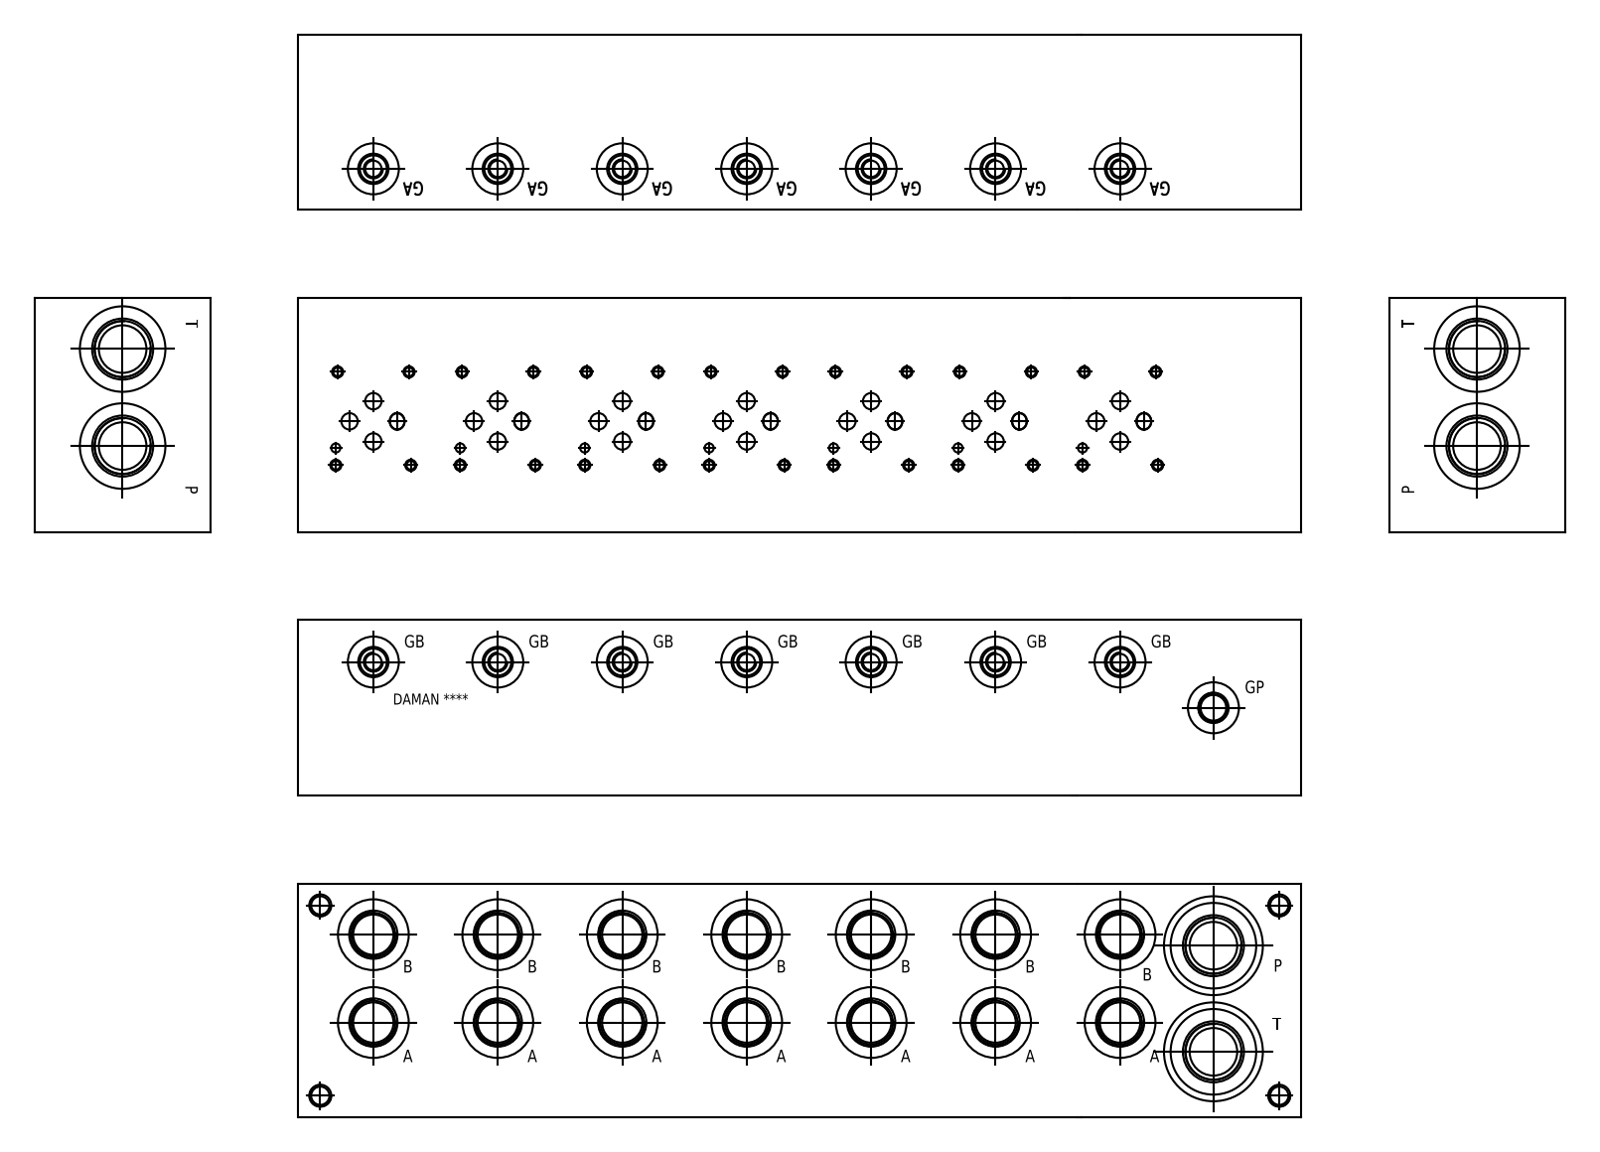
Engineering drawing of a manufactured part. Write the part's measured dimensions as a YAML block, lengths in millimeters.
part_name: "Part_AD03PB072B_3D"
step_written_by: "Autodesk Inventor 2020 (AUTOMOTIVE_DESIGN)"
units: millimeters
bodies: {solids: 1, faces: 1803, planar: 881, cylindrical: 241, other: 681}
overall_size: [434.98, 101.6, 76.2]
volume: 3079000
surface_area: 232554
round_holes:
  - {diameter: 7.14, count: 35}
  - {diameter: 4.22, count: 28}
  - {diameter: 5, count: 28}
  - {diameter: 11.68, count: 15}
  - {diameter: 13.26, count: 15}
  - {diameter: 22.12, count: 15}
  - {diameter: 17.48, count: 14}
  - {diameter: 21.06, count: 14}
  - {diameter: 30.68, count: 14}
  - {diameter: 18.92, count: 12}
  - {diameter: 3.96, count: 7}
  - {diameter: 6.35, count: 7}
face_to_face_distances: [76.2, 101.6, 0.79, 434.98, 75.41, 100.81, 434.19, 100.02, 5.56, 4.77]
hole_center_spacings: [107.95, 53.97, 53.98, 215.9, 161.93, 161.92, 114.48, 0.4]
